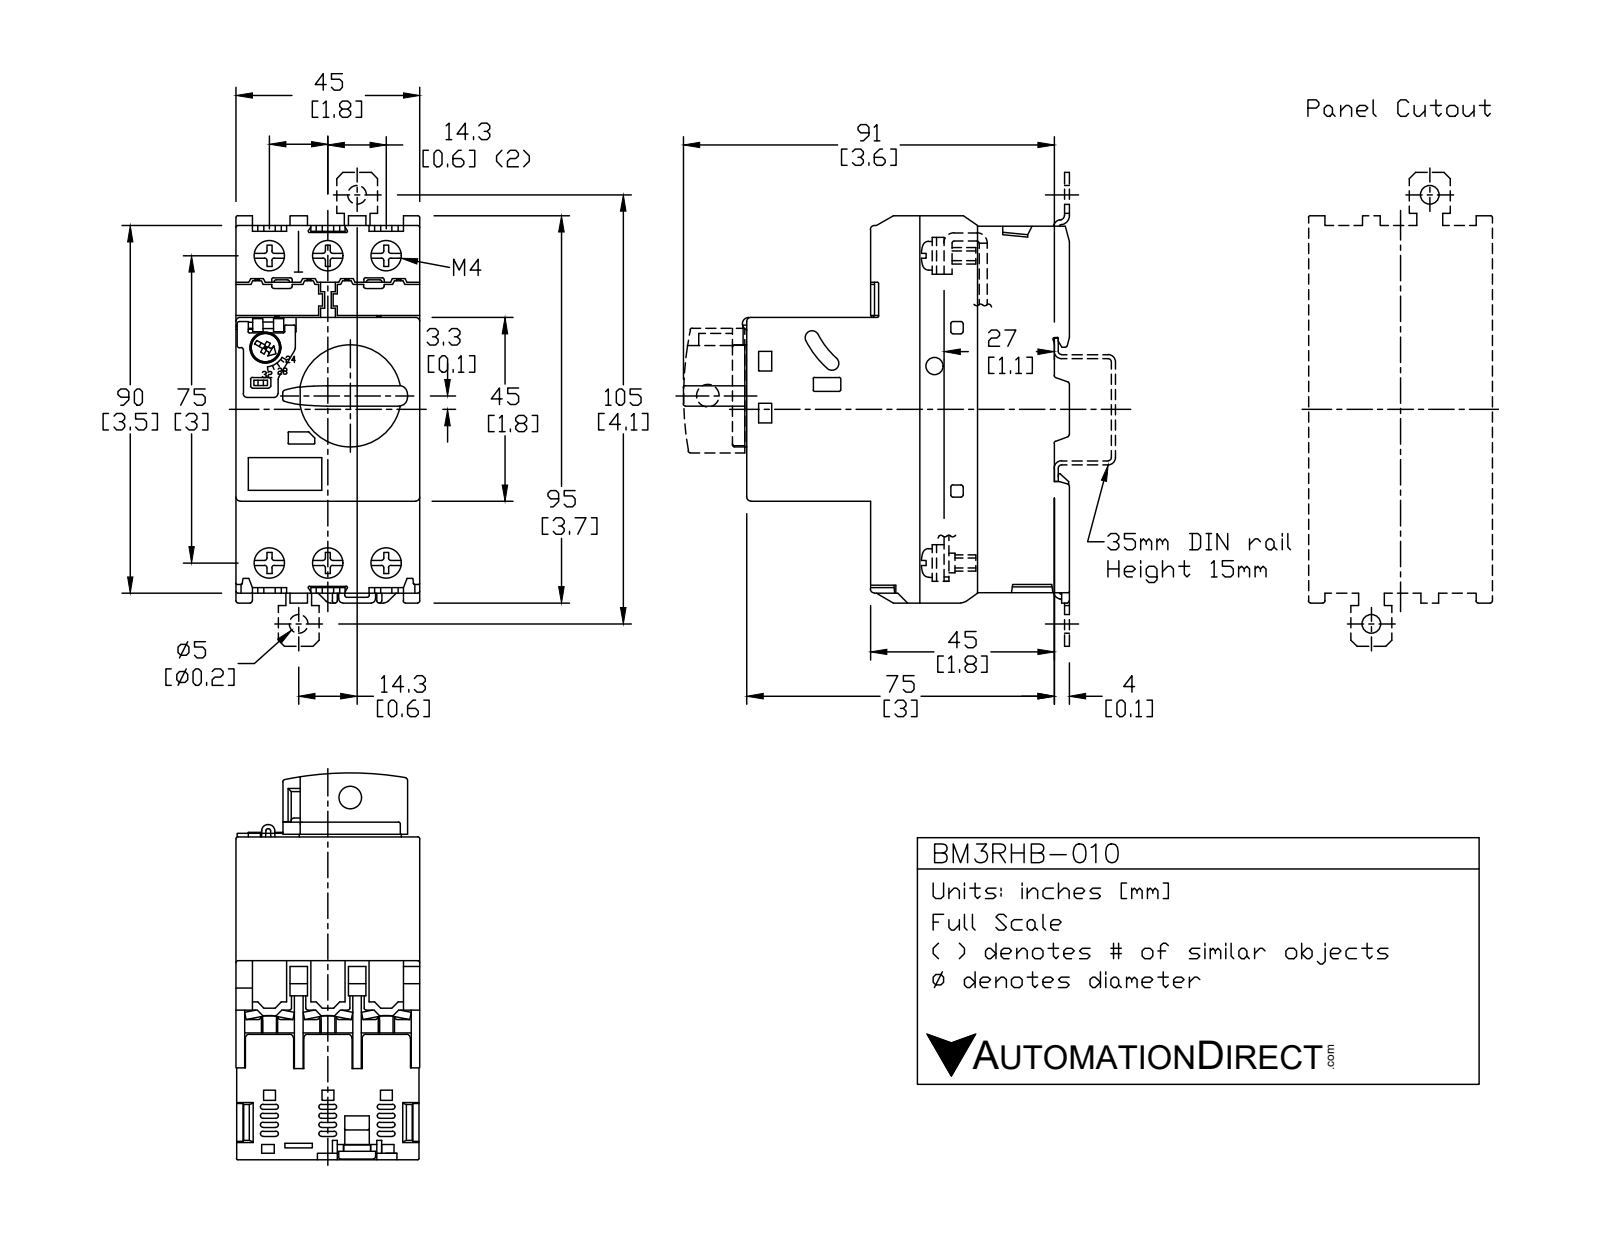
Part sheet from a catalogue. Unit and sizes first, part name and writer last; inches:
Units: inches
Overall size (bounding box): 3.732 × 3.72 × 1.772
Round holes (diameter × count): ⌀0.157 ×6, ⌀0.291 ×6, ⌀0.063 ×1, ⌀0.165 ×1, ⌀0.197 ×1, ⌀0.217 ×1, ⌀0.295 ×1
Round bosses / shafts (diameter × count): ⌀0.236 ×6, ⌀0.984 ×1, ⌀0.276 ×1
Partial cylindrical surfaces — rounded edges, fillets, slot ends (radius × count): R0.02 ×67, R0.024 ×24, R0.079 ×14, R0.012 ×12, R0.039 ×8, R0.098 ×8, R0.008 ×6, R0.059 ×2
Main face-to-face distances: 1.772, 1.441, 1.669, 3.11, 0.882, 2.654, 0.118, 0.65, 0.791, 0.472
Hole centre spacings: 0.563, 3.006, 2.953, 1.126, 3.16, 0.883, 0.941, 1.068
Volume: 14.13 in³ · Surface area: 88.41 in²
Bodies: 25 solids, 1294 faces (964 planar, 327 cylindrical, 3 other)
Part name (STEP PRODUCT): BM3RHB-010
STEP written by: SolidWorks 2018 (AUTOMOTIVE_DESIGN)
